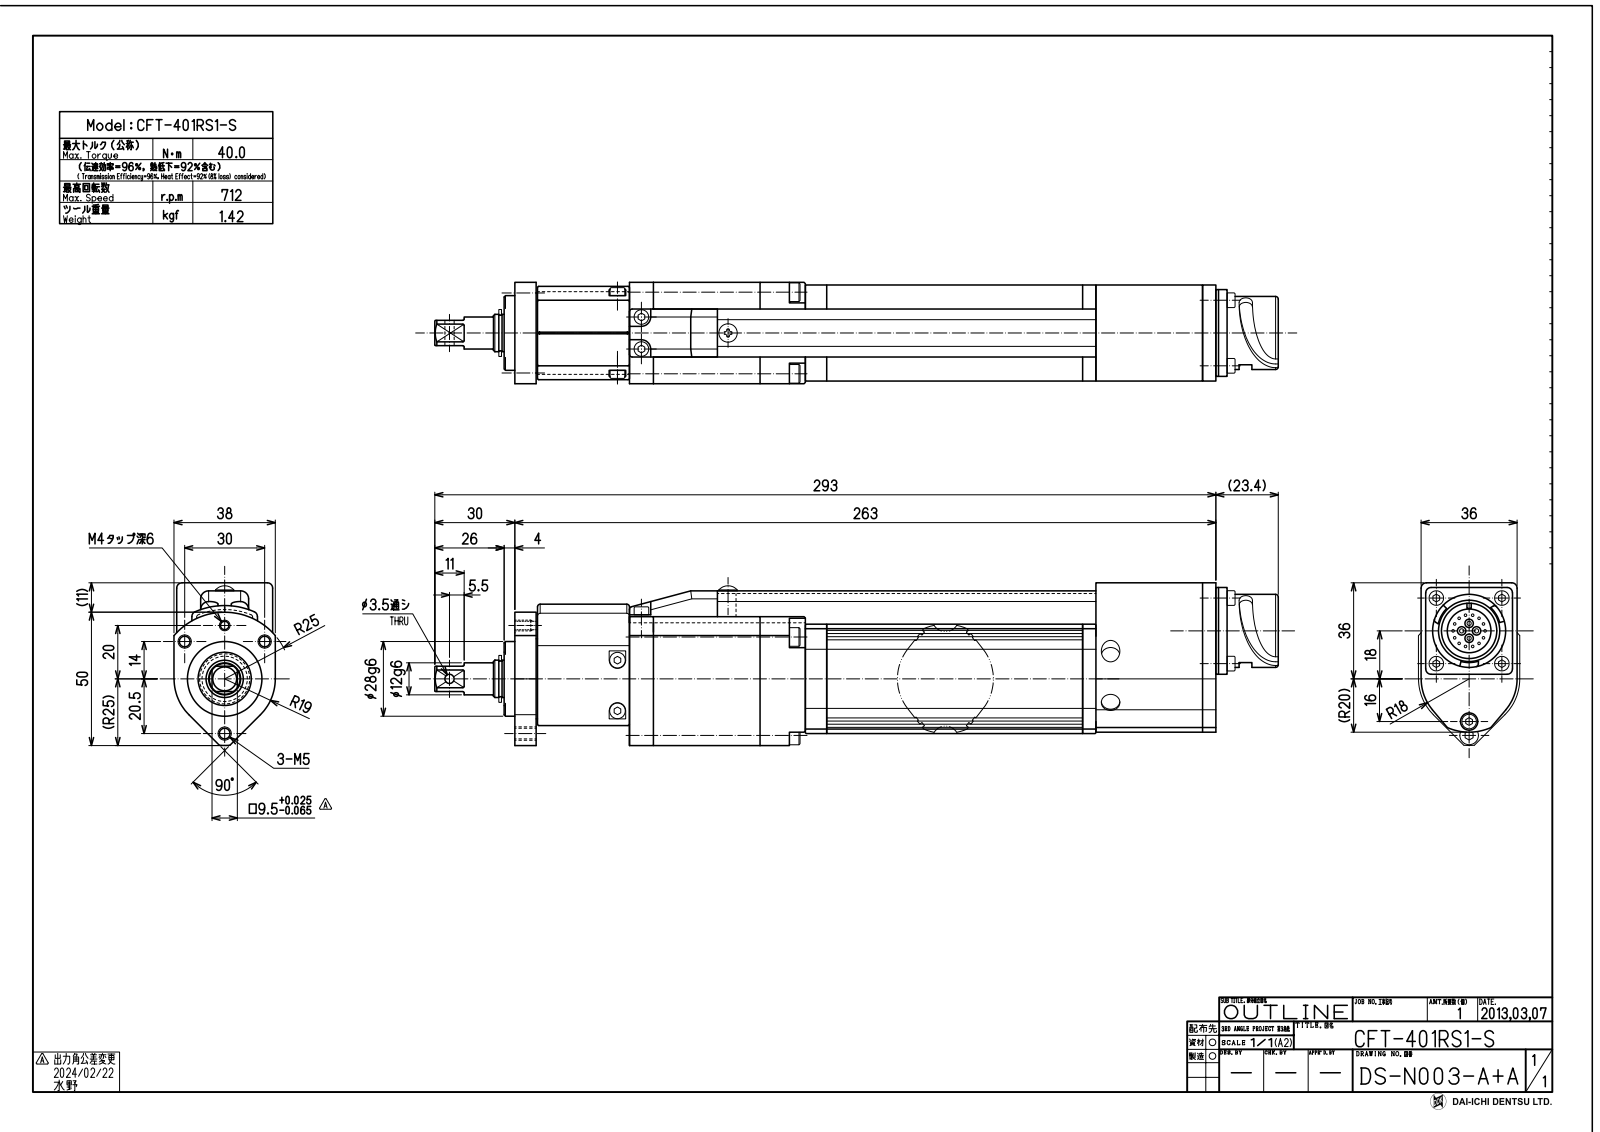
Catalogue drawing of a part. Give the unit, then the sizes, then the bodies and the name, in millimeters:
Units: millimetres
Overall size (bounding box): 315.4 × 61 × 38.1
Round holes (diameter × count): ⌀4.2 ×3, ⌀3.3 ×1, ⌀3.5 ×1, ⌀20.8 ×1
Round bosses / shafts (diameter × count): ⌀5.5 ×6, ⌀7.5 ×3, ⌀32 ×1, ⌀28 ×1, ⌀27.4 ×1, ⌀14 ×1, ⌀12 ×1, ⌀6.6 ×1
Partial cylindrical surfaces — rounded edges, fillets, slot ends (radius × count): R2 ×12, R0.5 ×7, R1 ×4, R3 ×4, R4.5 ×3, R3.5 ×2, R5 ×2, R18 ×1
Main face-to-face distances: 1, 109, 9, 27, 205, 10, 17, 44, 101, 8
Hole centre spacings: 15.81, 16.16, 37.62, 1, 30, 39.5, 40.5
Volume: 377 630 mm³ · Surface area: 86 744 mm²
Bodies: 17 solids, 326 faces (140 planar, 136 cylindrical, 50 other)
Part name (STEP PRODUCT): CFT-401RS1-S
STEP written by: SolidWorks 2013 (CONFIG_CONTROL_DESIGN)
